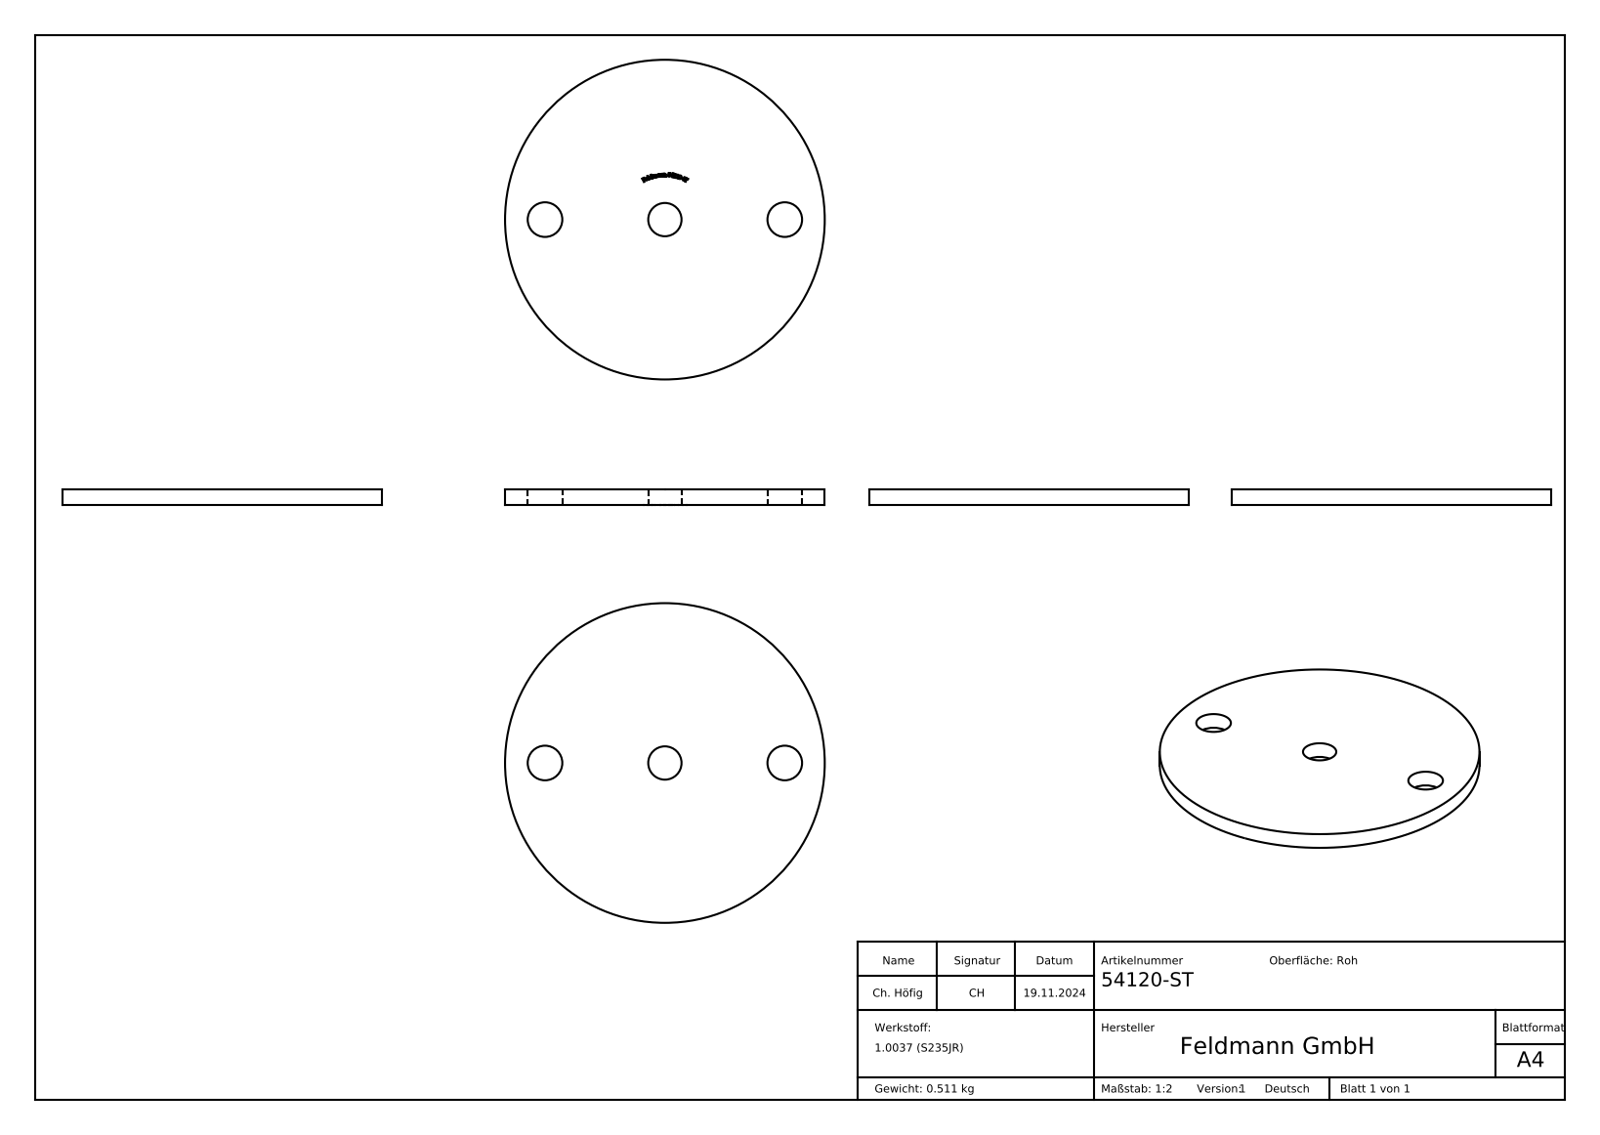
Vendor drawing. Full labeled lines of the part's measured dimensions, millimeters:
Part name (STEP PRODUCT): 54120-ST
STEP written by: SolidWorks 2018 (CONFIG_CONTROL_DESIGN)
Units: millimetres
Bodies: 1 solid, 212 faces (122 planar, 4 cylindrical, 86 other)
Overall size (bounding box): 120 × 120 × 6
Volume: 65 529 mm³ · Surface area: 24 839 mm²
Round holes (diameter × count): ⌀13 ×2, ⌀12.5 ×1
Round bosses / shafts (diameter × count): ⌀120 ×1
Main face-to-face distances: 6, 5.9, 1.33, 0.54, 0.85, 0.72, 0.6, 1.2, 1.46, 0.67
Hole centre spacings: 45, 90
